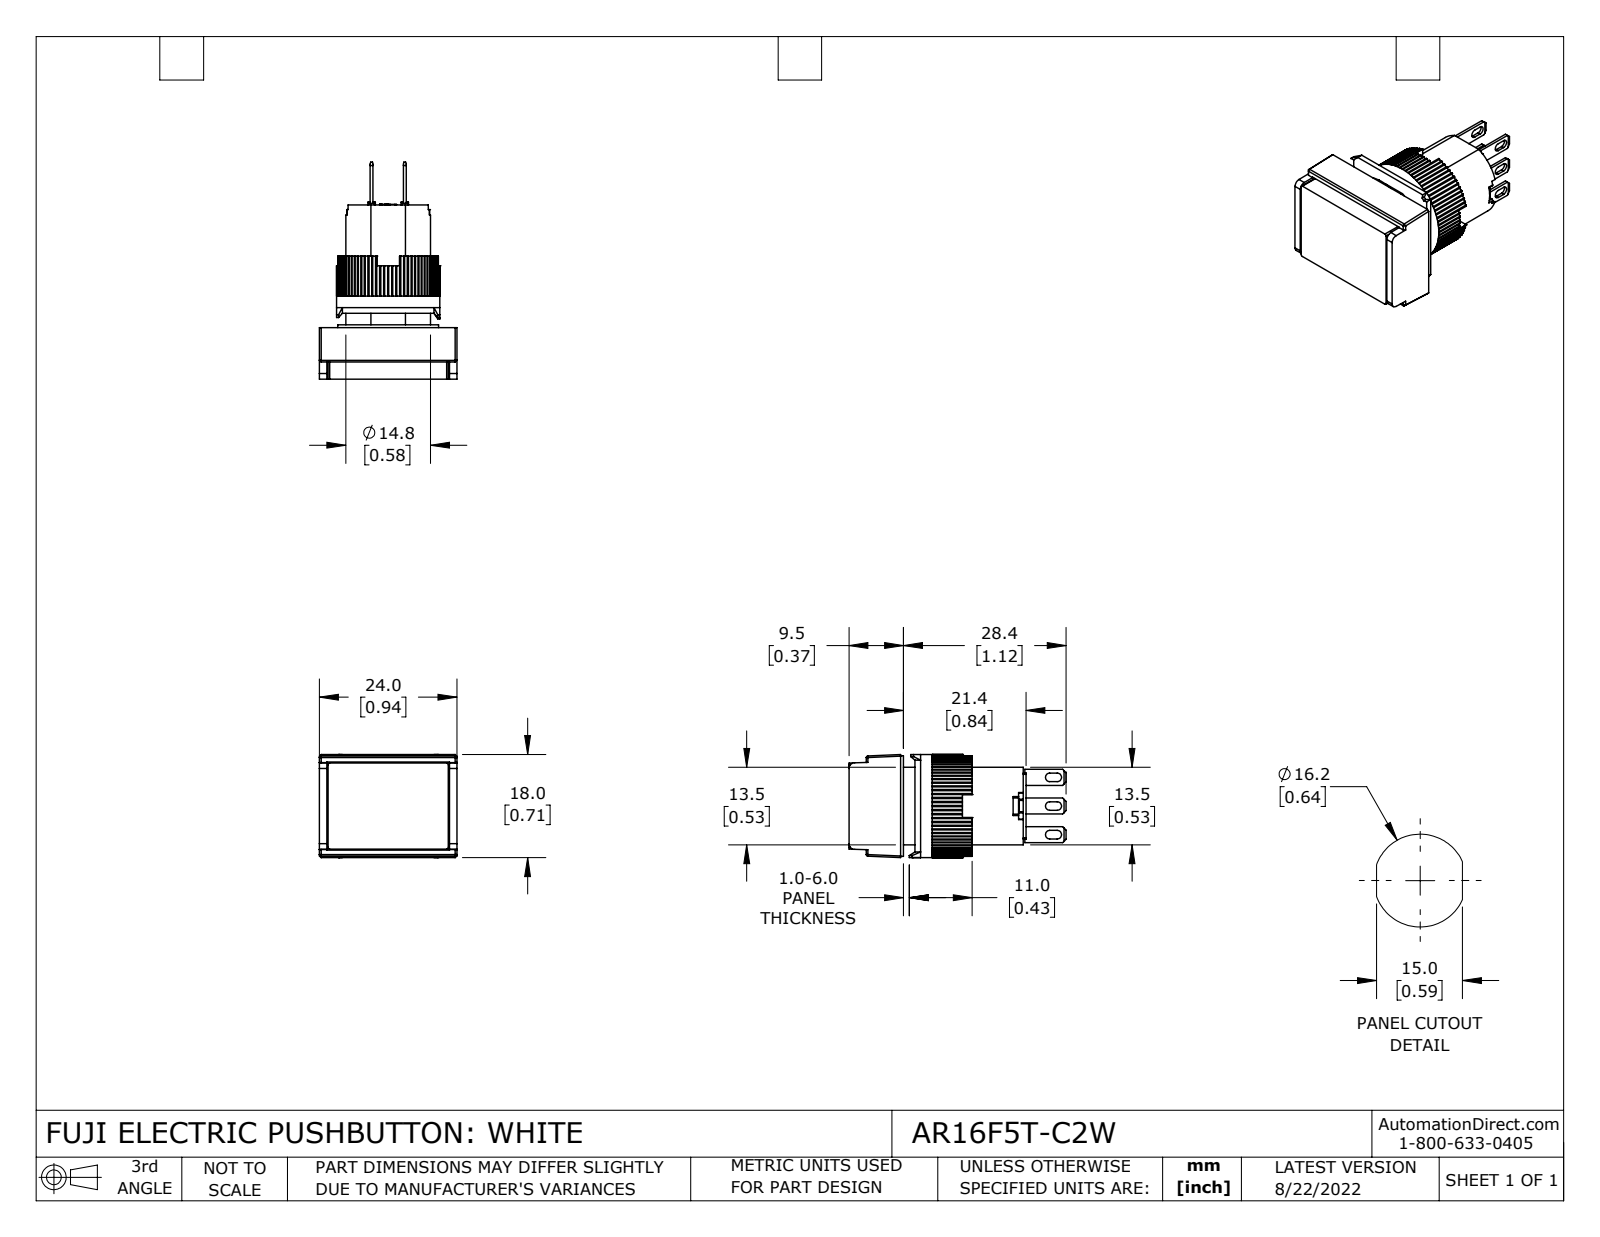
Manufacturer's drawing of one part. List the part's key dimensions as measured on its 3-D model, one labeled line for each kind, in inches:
Part name (STEP PRODUCT): AR16F5T-C2W
STEP written by: SolidWorks 2021 (CONFIG_CONTROL_DESIGN)
Units: inches
Bodies: 12 solids, 813 faces (632 planar, 177 cylindrical, 4 other)
Overall size (bounding box): 1.492 × 0.945 × 0.709
Volume: 0.443 in³ · Surface area: 9.124 in²
Round holes (diameter × count): ⌀0.543 ×1, ⌀0.583 ×1
Round bosses / shafts (diameter × count): ⌀0.709 ×1, ⌀0.693 ×1
Partial cylindrical surfaces — rounded edges, fillets, slot ends (radius × count): R0.01 ×80, R0.008 ×12, R0.012 ×6, R0.03 ×6, R0.039 ×2
Main face-to-face distances: 0.213, 0.354, 0.142, 0.492, 0.35, 0.138, 0.02, 0.843, 0.059, 0.453
